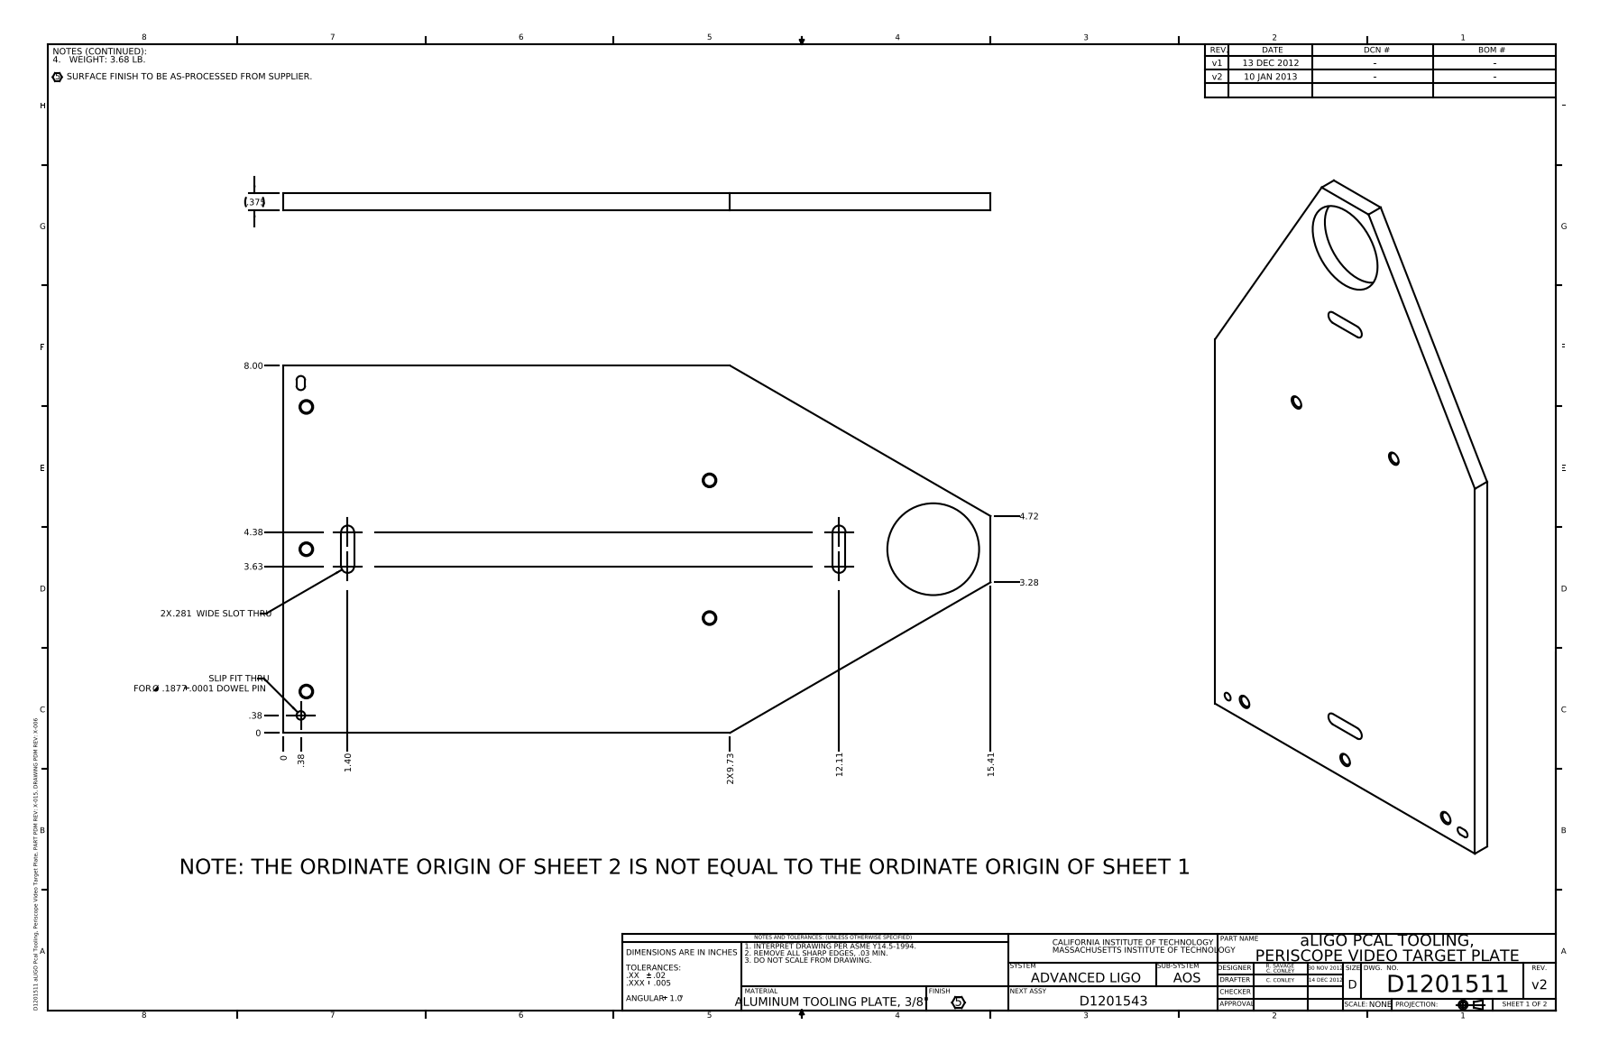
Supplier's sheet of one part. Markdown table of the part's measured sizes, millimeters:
| quantity | value |
| --- | --- |
| part name | D1201511-v2 aLIGO Pcal Tooling, Periscope Video Target Plate |
| STEP written by | SolidWorks 2012 (AUTOMOTIVE_DESIGN) |
| units | millimeters |
| bodies | 1 solid, 57 faces (14 planar, 23 cylindrical, 20 other) |
| overall size | 391.4 × 203.2 × 9.5 |
| volume | 618 600 mm³ |
| surface area | 143 900 mm² |
| round holes (diameter × count) | 6.4 × 5, 4.8 × 1, 50.8 × 1 |
| partial cylindrical surfaces (radius × count) | 3.6 × 4, 2.4 × 2 |
| main face-to-face distances | 9.5, 203.2, 391.4, 32, 39.1, 304, 311.2, 7.1, 272, 279.2 |
| hole center spacings | 78.7, 129.5, 226.4, 226.8, 251.9, 355.8, 13.6, 76.2 |
